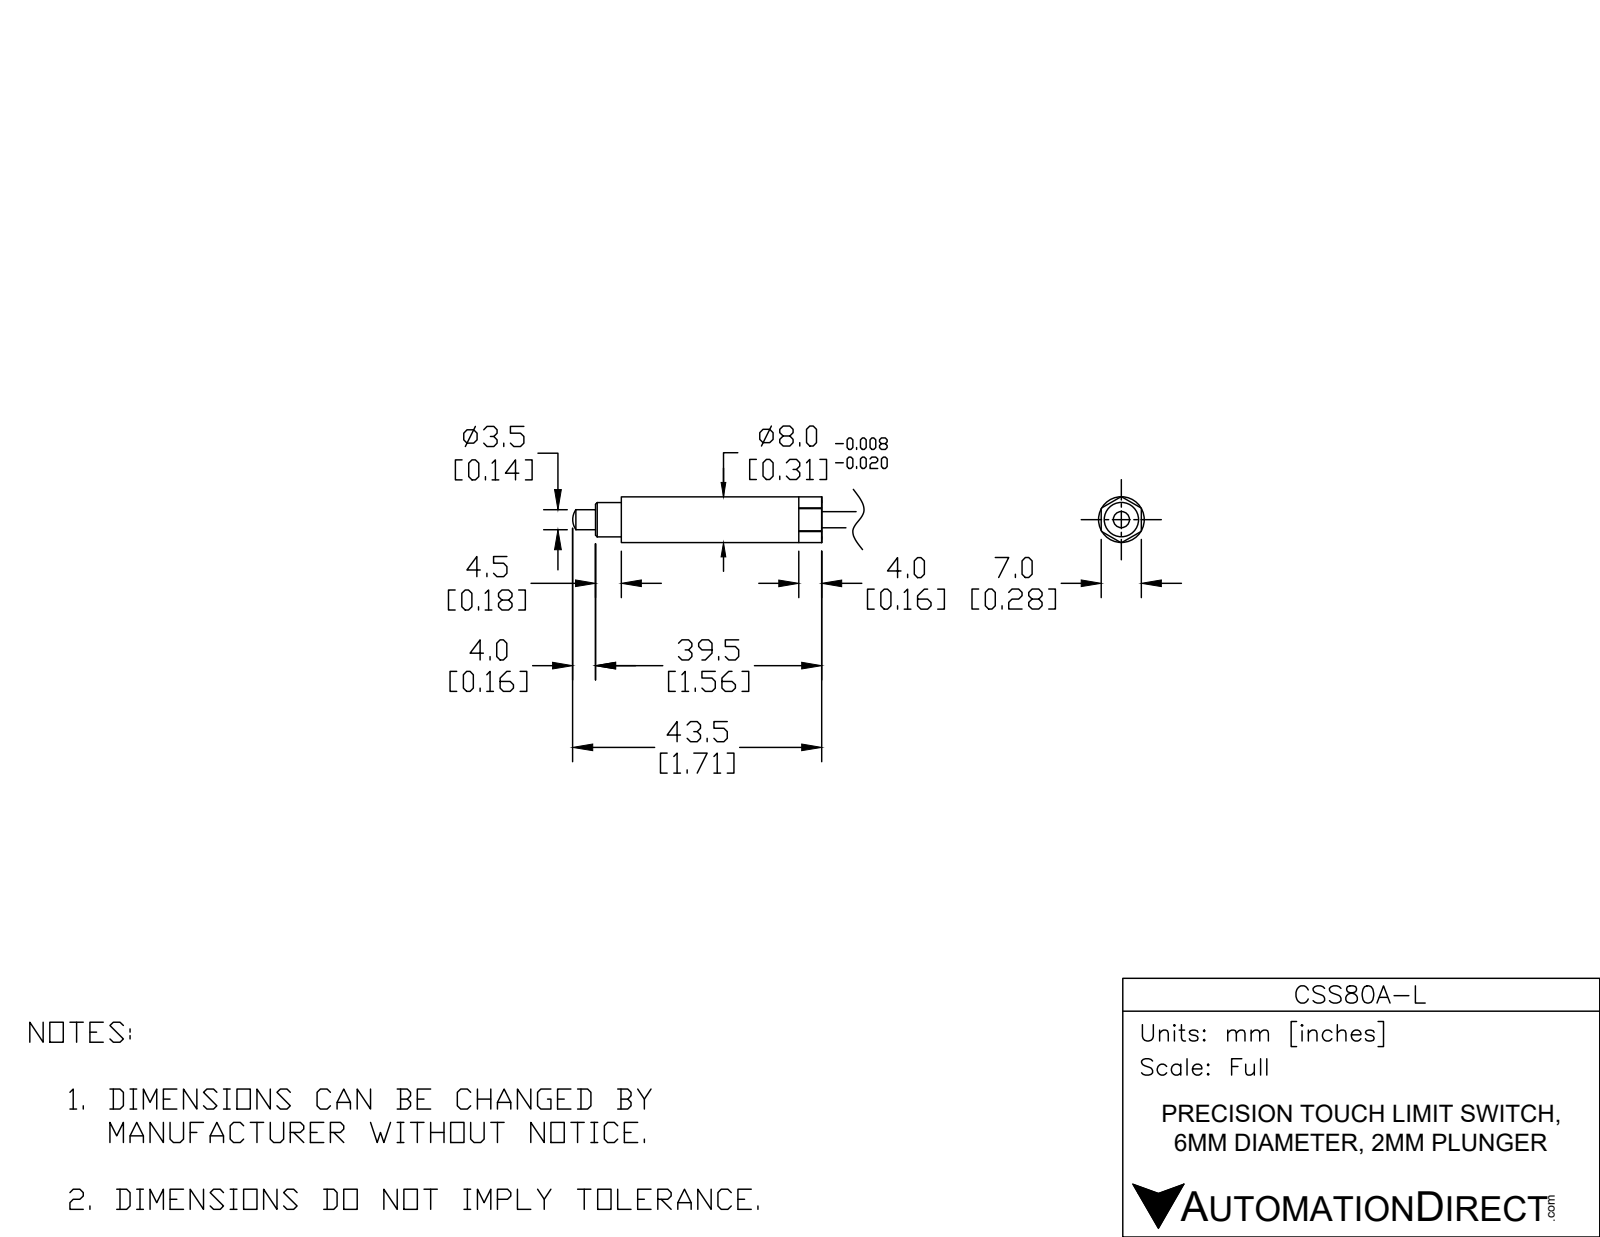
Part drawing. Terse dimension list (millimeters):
written by: Spatial InterOp 3D (CONFIG_CONTROL_DESIGN)
unit: mm
bodies: 1 solid, 28 faces (16 planar, 8 cylindrical, 4 other)
size: 49.5 × 8 × 8
volume: 1 927 mm³; area: 1 149 mm²
bosses: 1× ⌀8, 1× ⌀6, 1× ⌀3.5, 1× ⌀2.8
face distances: 7, 35, 4.5, 39.5, 35.5, 31, 4, 45.5, 41, 10
